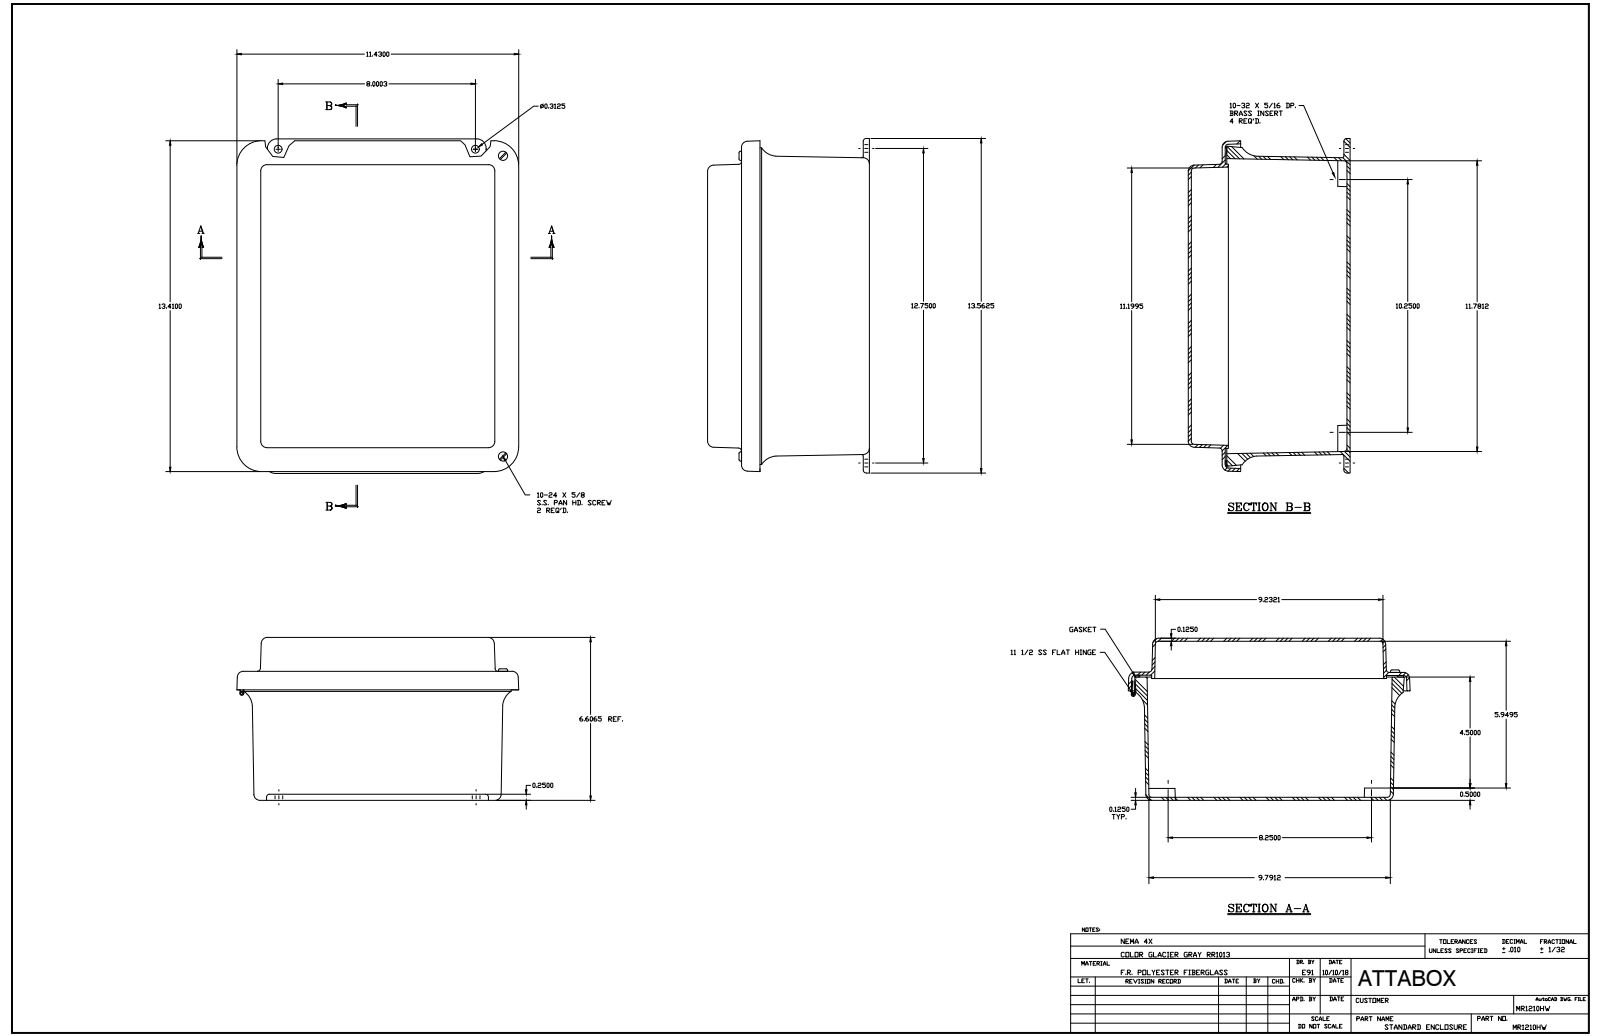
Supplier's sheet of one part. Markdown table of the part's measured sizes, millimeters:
| quantity | value |
| --- | --- |
| part name | MR1210HW |
| STEP written by | SolidWorks 2018 (AUTOMOTIVE_DESIGN) |
| units | millimeters |
| bodies | 22 solids, 858 faces (306 planar, 323 cylindrical, 229 other) |
| overall size | 344.5 × 290.9 × 167.3 |
| volume | 1 500 000 mm³ |
| surface area | 823 900 mm² |
| round holes (diameter × count) | 3.3 × 8, 3.6 × 8, 3.9 × 5, 4 × 4, 5.5 × 4, 3.7 × 2, 2.2 × 1, 2.2 × 1 |
| round bosses / shafts (diameter × count) | 6.4 × 8, 6.9 × 6, 3.2 × 4, 3.2 × 4, 4.8 × 2, 4 × 2, 3.9 × 1, 3.9 × 1 |
| partial cylindrical surfaces (radius × count) | 0.8 × 20, 3.2 × 20, 6.4 × 12, 5.1 × 4, 7.2 × 4, 8 × 4, 9.5 × 4, 19.1 × 4 |
| main face-to-face distances | 3.2, 164.2, 167.3, 161, 128.9, 35.2, 125.7, 38.4, 132.1, 32.1 |
| hole center spacings | 92.1, 34.2, 235, 285.6, 368.2, 6.4, 92.1, 174.6 |
